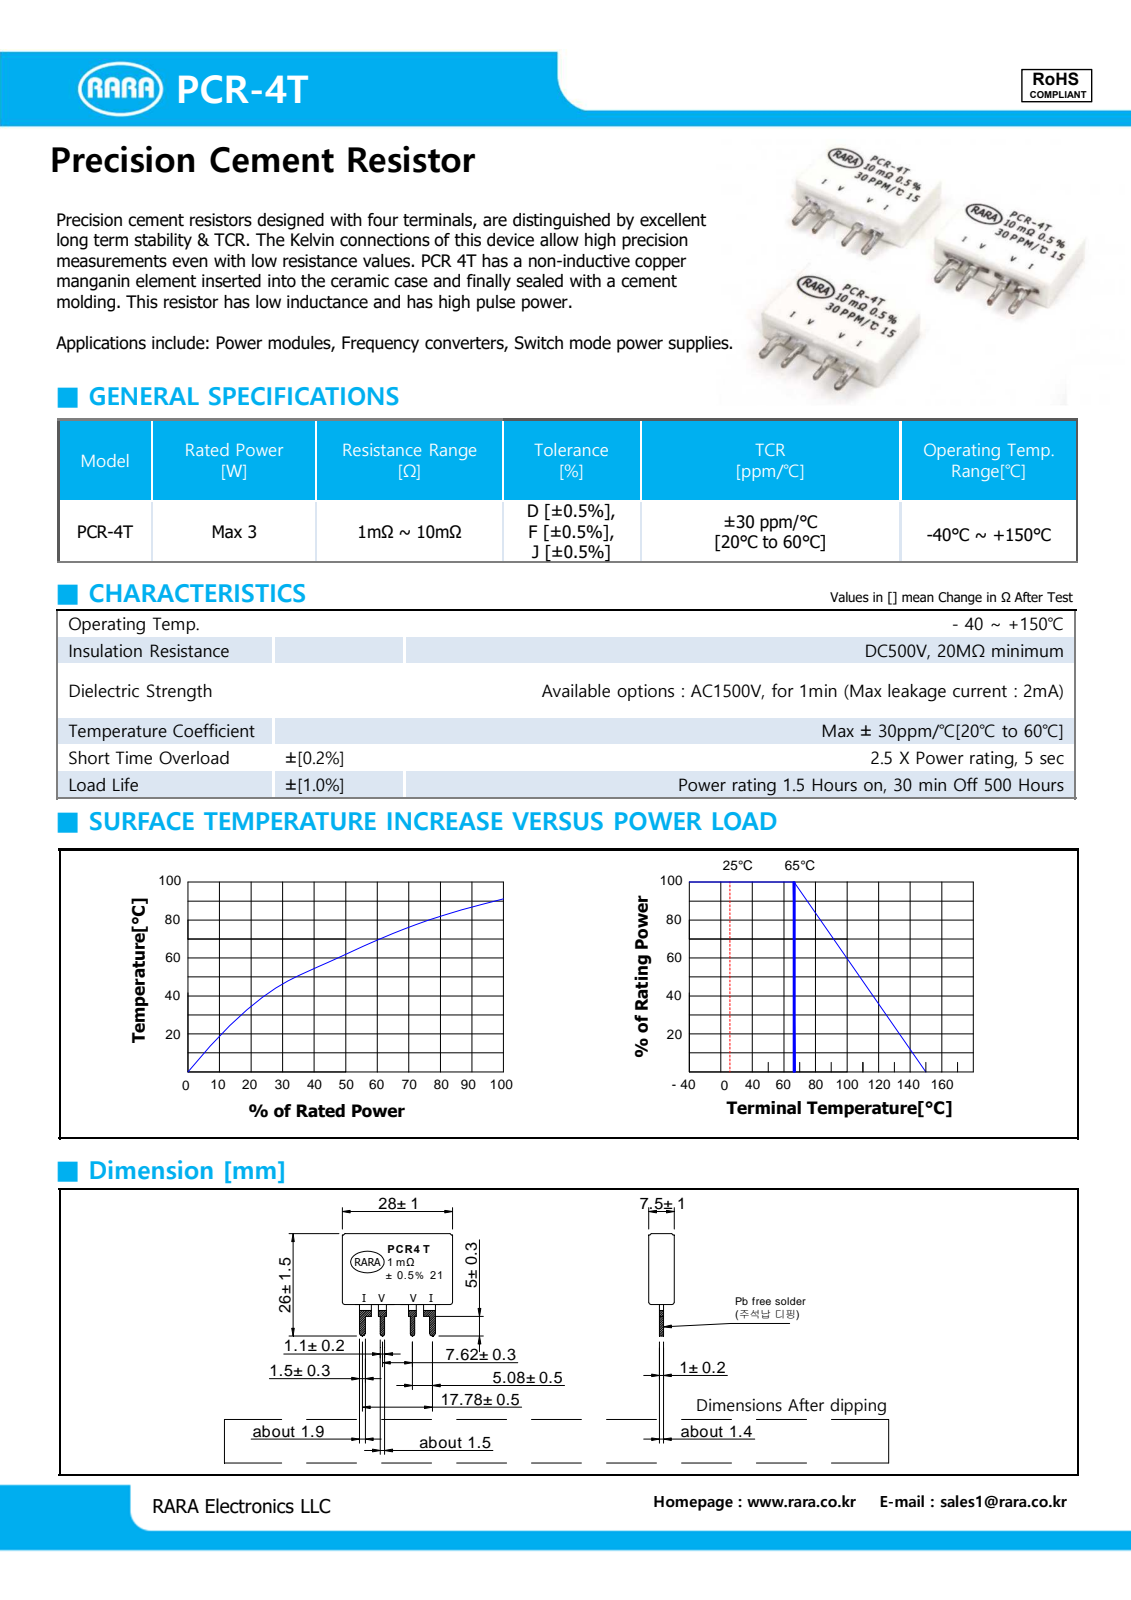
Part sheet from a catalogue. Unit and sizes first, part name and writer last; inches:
Units: inches
Overall size (bounding box): 1.102 × 1.028 × 0.295
Partial cylindrical surfaces — rounded edges, fillets, slot ends (radius × count): R0.004 ×12, R0.02 ×8, R0.024 ×4, R0.022 ×2, R0.03 ×2
Main face-to-face distances: 0.098, 0.197, 0.295, 0.024, 0.122, 0.173, 0.075, 0.728, 1.102, 0.051
Volume: 0.237 in³ · Surface area: 5.527 in²
Bodies: 6 solids, 121 faces (65 planar, 44 cylindrical, 12 other)
Part name (STEP PRODUCT): PCR4T 25.09.10
STEP written by: SolidWorks 2018 (CONFIG_CONTROL_DESIGN)
